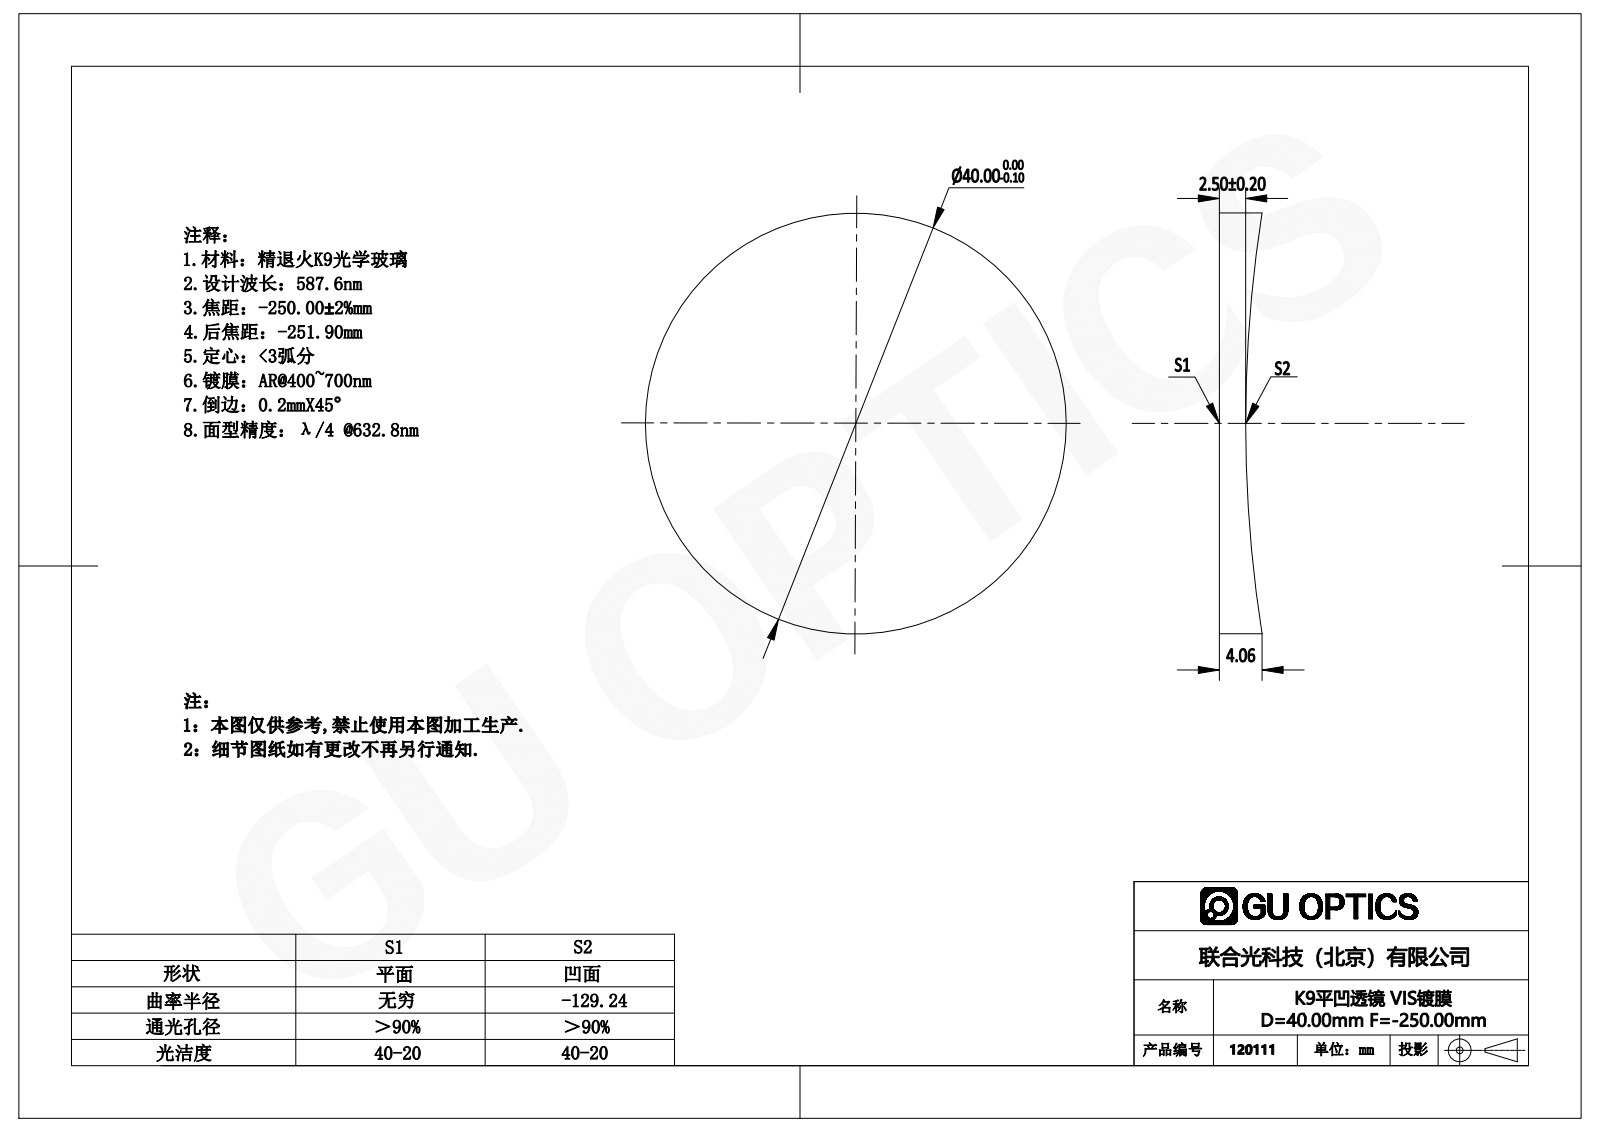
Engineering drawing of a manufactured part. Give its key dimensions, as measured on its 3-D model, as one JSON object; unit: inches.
{"part_name": "120051", "step_written_by": "SolidWorks 2016 (AUTOMOTIVE_DESIGN)", "units": "inches", "bodies": {"solids": 1, "faces": 5, "planar": 1, "cylindrical": 2, "other": 2}, "overall_size": [1.575, 1.575, 0.16], "volume_in3": 0.251, "surface_area_in2": 4.698, "round_bosses_or_shafts": [[1.575, 1]]}
